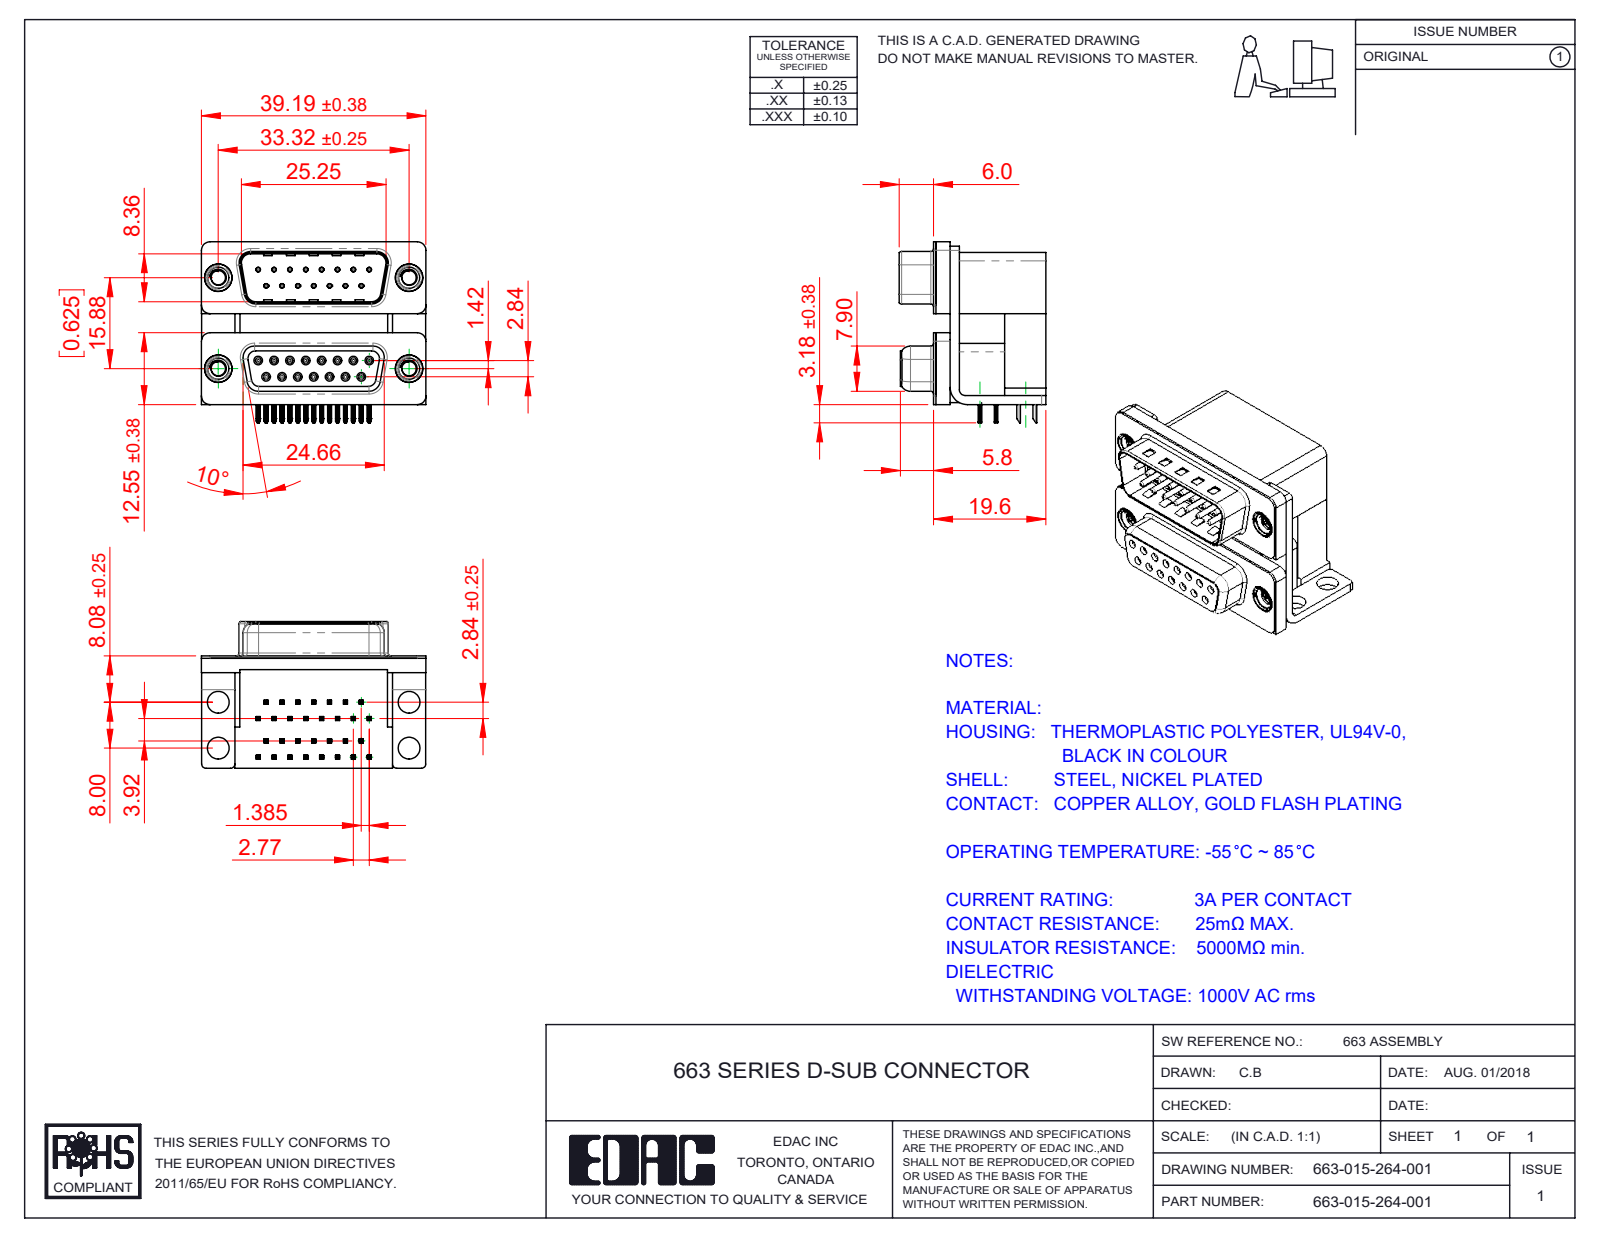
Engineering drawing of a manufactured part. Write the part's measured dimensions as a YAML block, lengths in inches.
part_name: "663 Contact Bottom Upper_L; 663 Contact Bottom Lower; 663 Threaded Rivet_M3; 663 Shell Plug_15 Contacts (+8 more)"
step_written_by: "SolidWorks 2020 (CONFIG_CONTROL_DESIGN)"
units: inches
bodies: {solids: 41, faces: 3916, planar: 2015, cylindrical: 1022, other: 879}
overall_size: [1.543, 1.244, 1.008]
volume: 0.889
surface_area: 24.99
round_holes:
  - {diameter: 0.031, count: 30}
  - {diameter: 0.014, count: 15}
  - {diameter: 0.035, count: 15}
  - {diameter: 0.098, count: 4}
  - {diameter: 0.138, count: 4}
  - {diameter: 0.15, count: 4}
  - {diameter: 0.157, count: 4}
  - {diameter: 0.189, count: 4}
  - {diameter: 0.197, count: 4}
round_bosses_or_shafts:
  - {diameter: 0.047, count: 15}
  - {diameter: 0.03, count: 15}
  - {diameter: 0.193, count: 4}
  - {diameter: 0.187, count: 4}
  - {diameter: 0.154, count: 4}
partial_cylinders:
  - {radius: 0.004, count: 120}
  - {radius: 0.006, count: 60}
  - {radius: 0.01, count: 60}
  - {radius: 0.005, count: 30}
  - {radius: 0.014, count: 30}
  - {radius: 0.059, count: 16}
  - {radius: 0.013, count: 15}
  - {radius: 0.02, count: 12}
face_to_face_distances: [0.016, 0.756, 0.657, 0.098, 0.421, 0.283, 0.472, 0.374, 0.114, 0.772]
hole_center_spacings: [0.124, 0.635, 0.109, 0.662, 0.218, 0.327, 0.625, 0.706]
